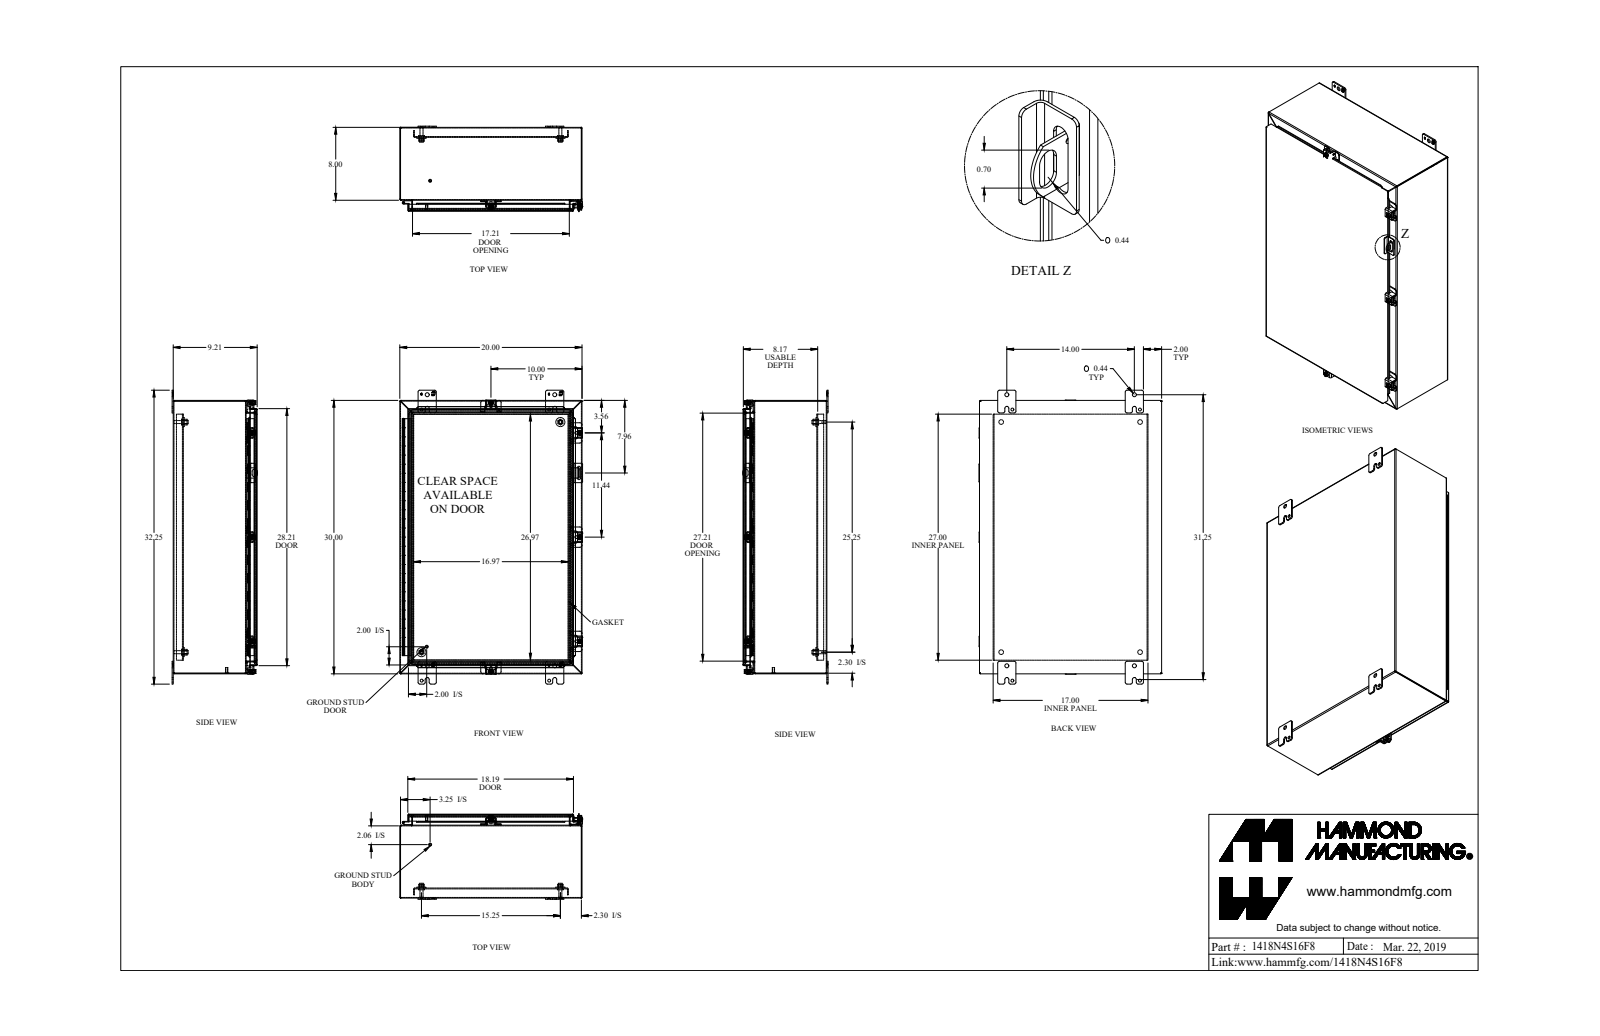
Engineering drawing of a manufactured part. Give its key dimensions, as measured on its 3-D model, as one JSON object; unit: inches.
{"part_name": "1418N4S16F8_Default", "step_written_by": "SolidWorks 2019 (CONFIG_CONTROL_DESIGN)", "units": "inches", "bodies": {"solids": 43, "faces": 1539, "planar": 827, "cylindrical": 572, "other": 140}, "overall_size": [32.25, 20.063, 9.375], "volume_in3": 223.3, "surface_area_in2": 5877, "round_holes": [[0.213, 5], [0.375, 5], [0.313, 4], [0.437, 4], [0.5, 4], [0.265, 3], [0.265, 2], [0.307, 2], [0.445, 2], [0.11, 1], [0.125, 1]], "round_bosses_or_shafts": [[0.5, 5], [0.39, 5], [0.244, 5], [0.65, 4], [0.375, 4], [0.332, 4], [1, 2], [0.313, 2]], "partial_cylinders_radius": [[0.048, 27], [0.143, 27], [0.188, 26], [0.036, 24], [0.108, 24], [0.25, 24], [0.125, 12], [0.141, 10]], "face_to_face_distances": [0.072, 9.066, 9.138, 0.072, 9.138, 0.937, 9.21, 0.095, 1.009, 19.928], "hole_center_spacings": [1.736, 7.916, 14, 28.417, 29.75, 32.88, 2.434, 3.065]}
